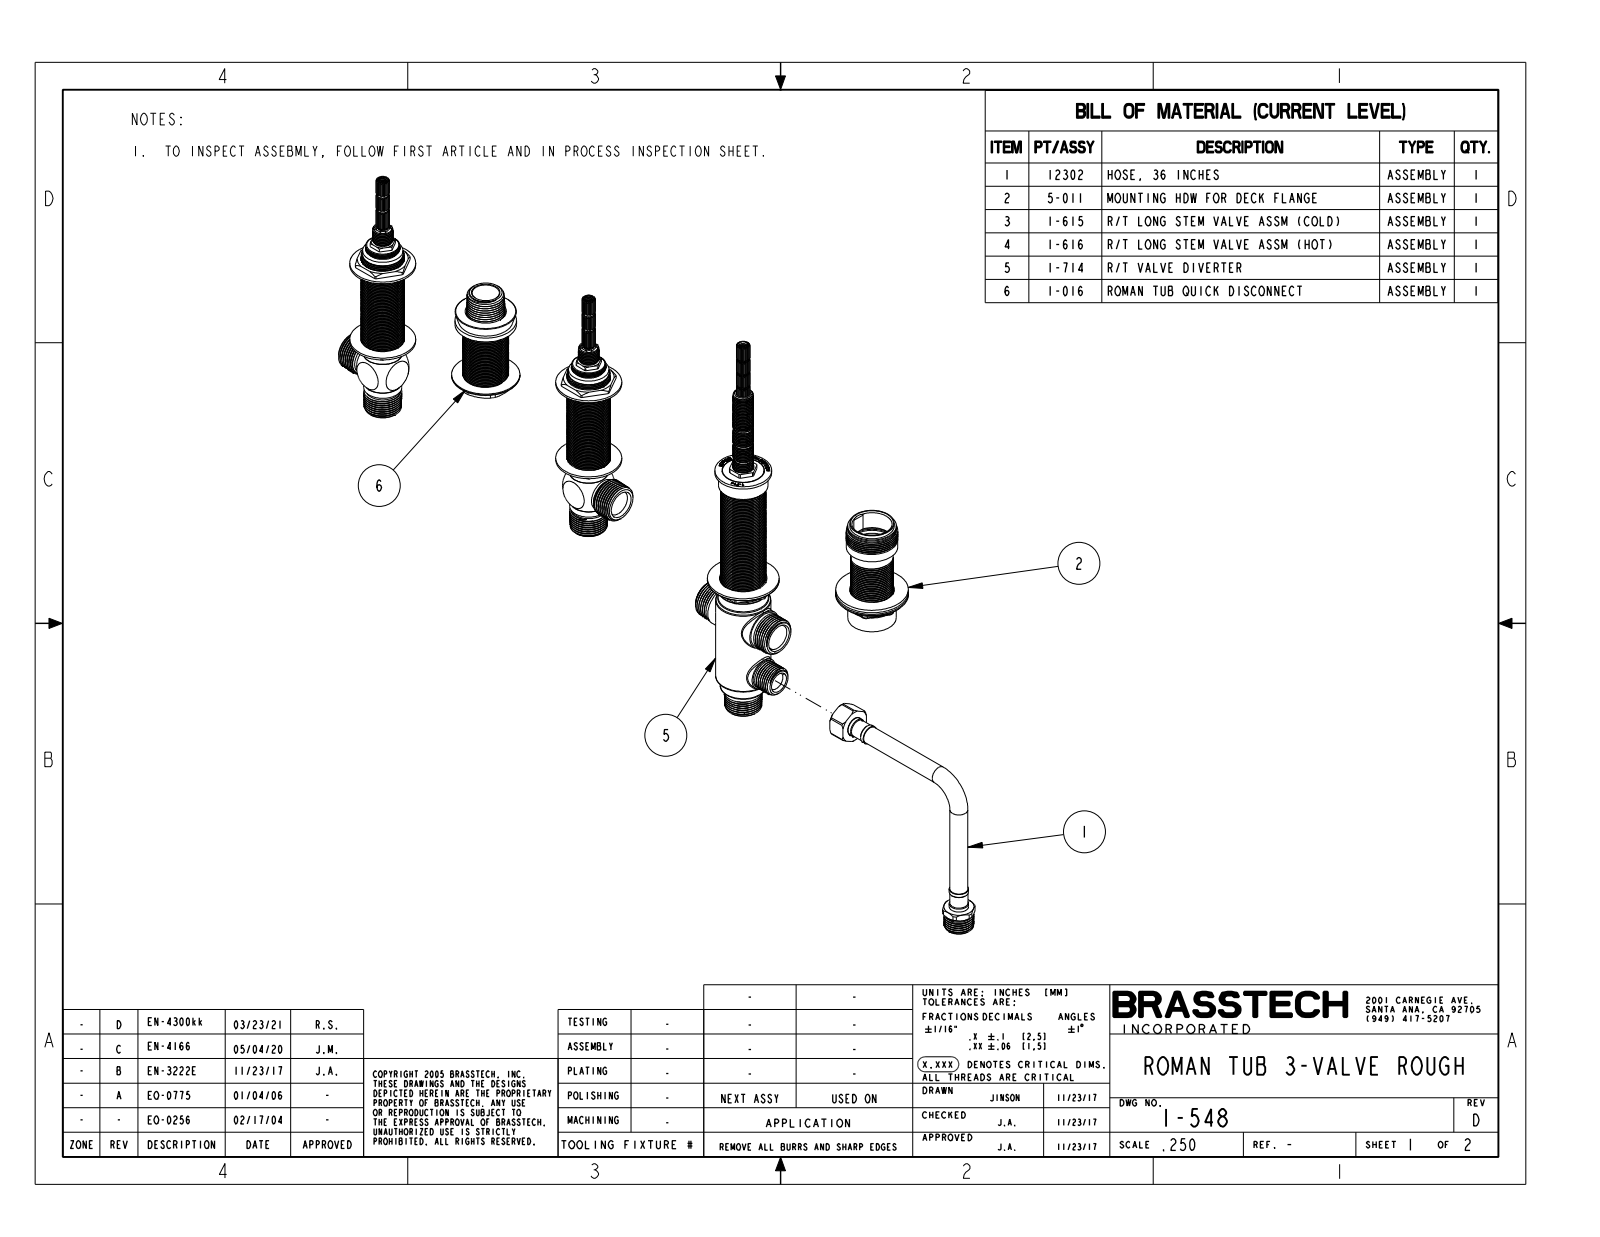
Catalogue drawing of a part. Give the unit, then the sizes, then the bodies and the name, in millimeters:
Units: millimetres
Overall size (bounding box): 543.9 × 391.3 × 50.8
Round holes (diameter × count): ⌀22.9 ×3, ⌀5.1 ×2, ⌀6 ×2, ⌀7 ×2, ⌀16.9 ×2, ⌀21.1 ×2, ⌀22.4 ×2, ⌀25.4 ×2, ⌀28.2 ×2, ⌀3.5 ×1, ⌀5.1 ×1, ⌀7 ×1
Round bosses / shafts (diameter × count): ⌀46 ×2, ⌀30.1 ×2, ⌀28.5 ×2, ⌀28.2 ×2, ⌀27.3 ×2, ⌀26.6 ×2, ⌀26.3 ×2, ⌀24 ×2
Partial cylindrical surfaces — rounded edges, fillets, slot ends (radius × count): R1 ×16, R2 ×8, R1 ×6, R3.8 ×6, R4.2 ×3, R1.3 ×2, R1.5 ×2, R4.7 ×2
Main face-to-face distances: 65, 1.5, 40.7, 22.8, 63.5, 57.6, 59.2, 72.6, 49.8, 9.1
Hole centre spacings: 101.6, 17.9, 74.3, 127, 144.9, 152.4, 203.2, 254
Volume: 565 200 mm³ · Surface area: 227 800 mm²
Bodies: 27 solids, 4300 faces (1038 planar, 1809 cylindrical, 1453 other)
Part name (STEP PRODUCT): 10173; 10172; 10174; 1-016_ASM (+8 more)
STEP written by: CREO PARAMETRIC BY PTC INC, 2018400 (AUTOMOTIVE_DESIGN)
